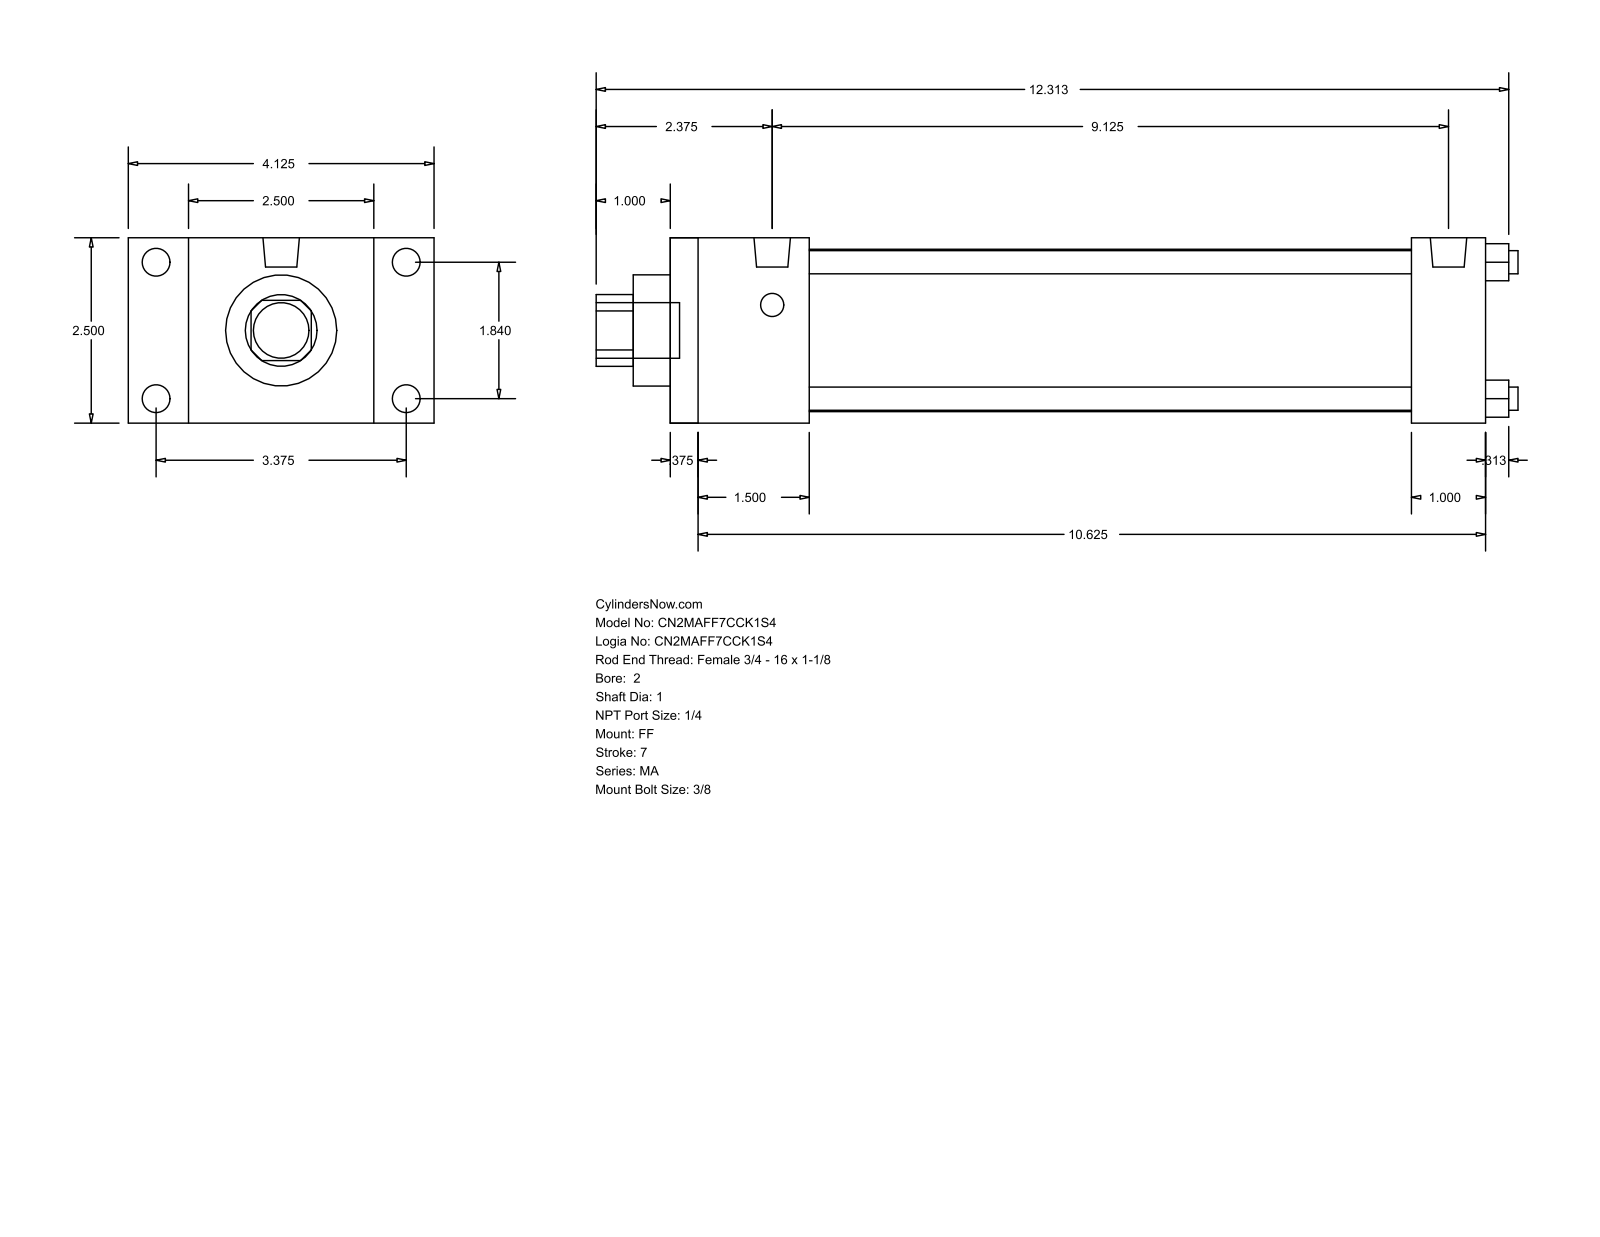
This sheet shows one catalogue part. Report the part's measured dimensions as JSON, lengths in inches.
{"part_name": "MA_FF__0200_1", "step_written_by": "GSSL Pune (CONFIG_CONTROL_DESIGN)", "units": "inches", "bodies": {"solids": 0, "faces": 92, "planar": 64, "cylindrical": 28, "other": 0}, "overall_size": [12.437, 4.125, 2.5], "round_holes": [[0.313, 4], [1, 1], [1.5, 1], [2.19, 1]], "round_bosses_or_shafts": [[0.375, 4], [0.313, 4], [0.492, 2], [0.75, 1]], "partial_cylinders_radius": [[0.484, 1]], "face_to_face_distances": [2.5, 11, 0.375, 10.625, 1, 0.813, 0.5, 1.875, 10, 1.5], "hole_center_spacings": [1.301, 1.84, 2.602]}
